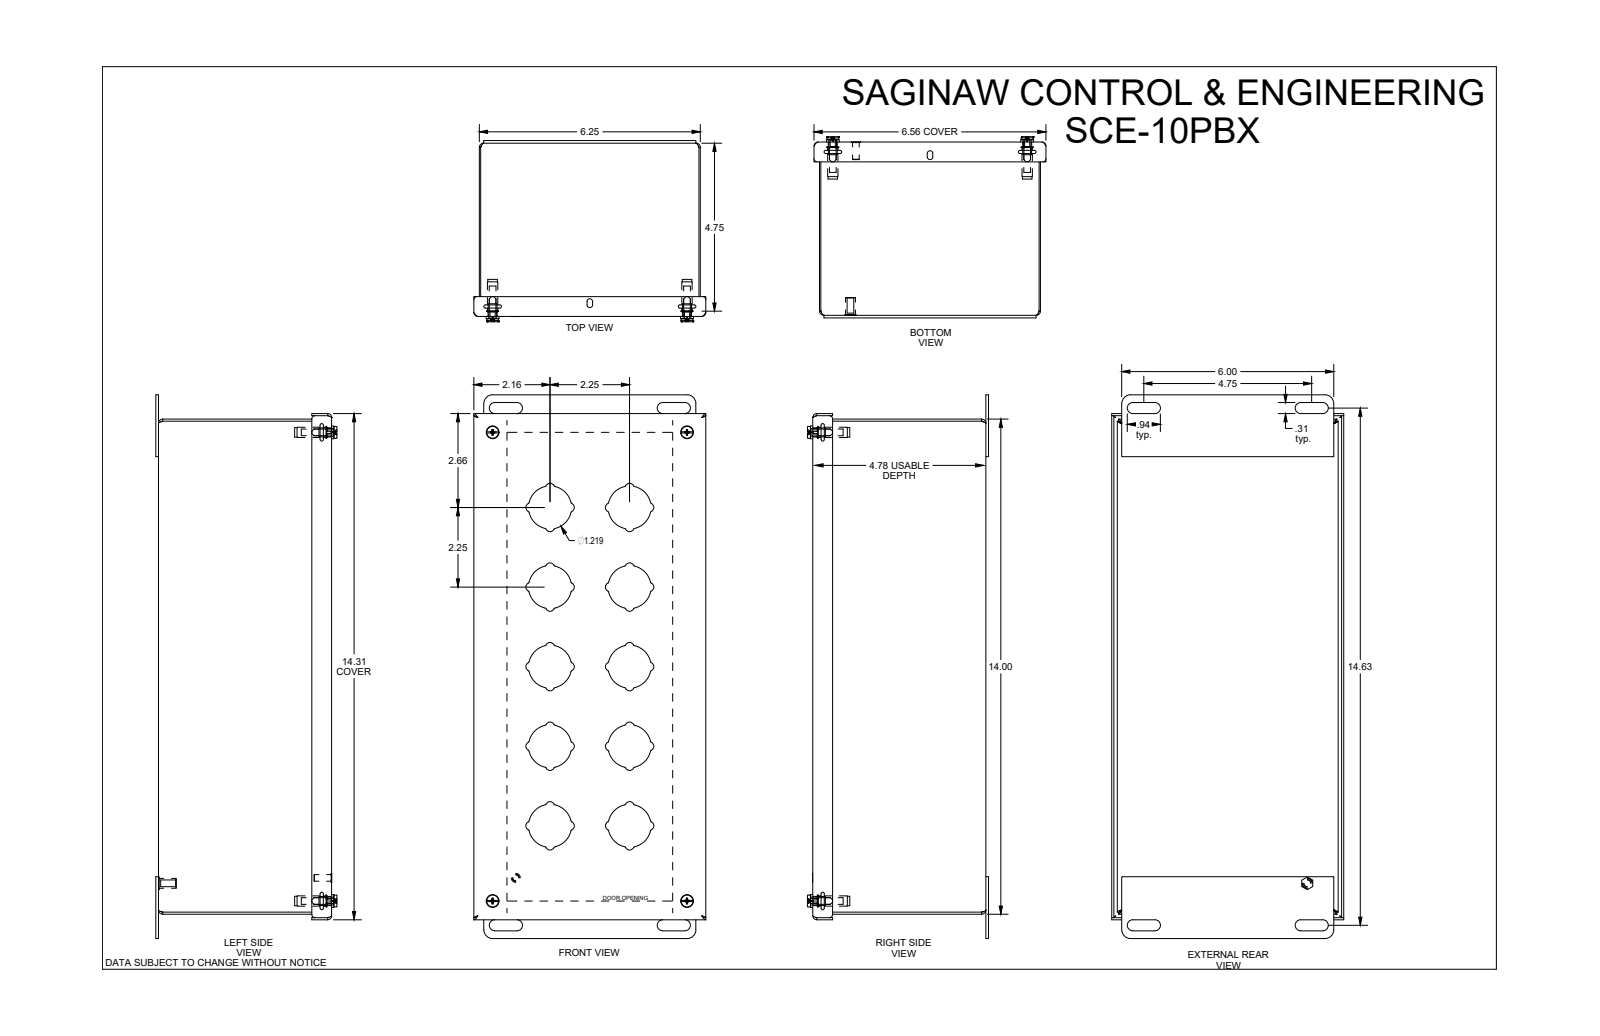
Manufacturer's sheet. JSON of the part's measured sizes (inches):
{"part_name": "SCE-10PBX", "step_written_by": "SolidWorks 2019 (AUTOMOTIVE_DESIGN)", "units": "inches", "bodies": {"solids": 15, "faces": 572, "planar": 162, "cylindrical": 334, "other": 76}, "overall_size": [15.375, 6.563, 5.036], "volume_in3": 26.58, "surface_area_in2": 883.4, "round_holes": [[0.19, 5], [0.22, 4], [0.25, 4], [0.266, 4], [0.317, 4], [0.193, 1], [0.281, 1]], "round_bosses_or_shafts": [[0.437, 4], [0.362, 4], [0.34, 4], [0.292, 4], [0.27, 4], [0.26, 4], [0.28, 1], [0.256, 1]], "partial_cylinders_radius": [[0.04, 80], [0.125, 40], [0.06, 20], [0.609, 10], [0.015, 8], [0.115, 8], [0.156, 8], [0.245, 8]], "face_to_face_distances": [0.06, 4.838, 6.19, 4.778, 4.898, 6.25, 6.13, 13.94, 4.69, 0.148], "hole_center_spacings": [5.5, 13.25, 14.346, 5.025, 5.5, 13.25, 13.25, 13.695]}
